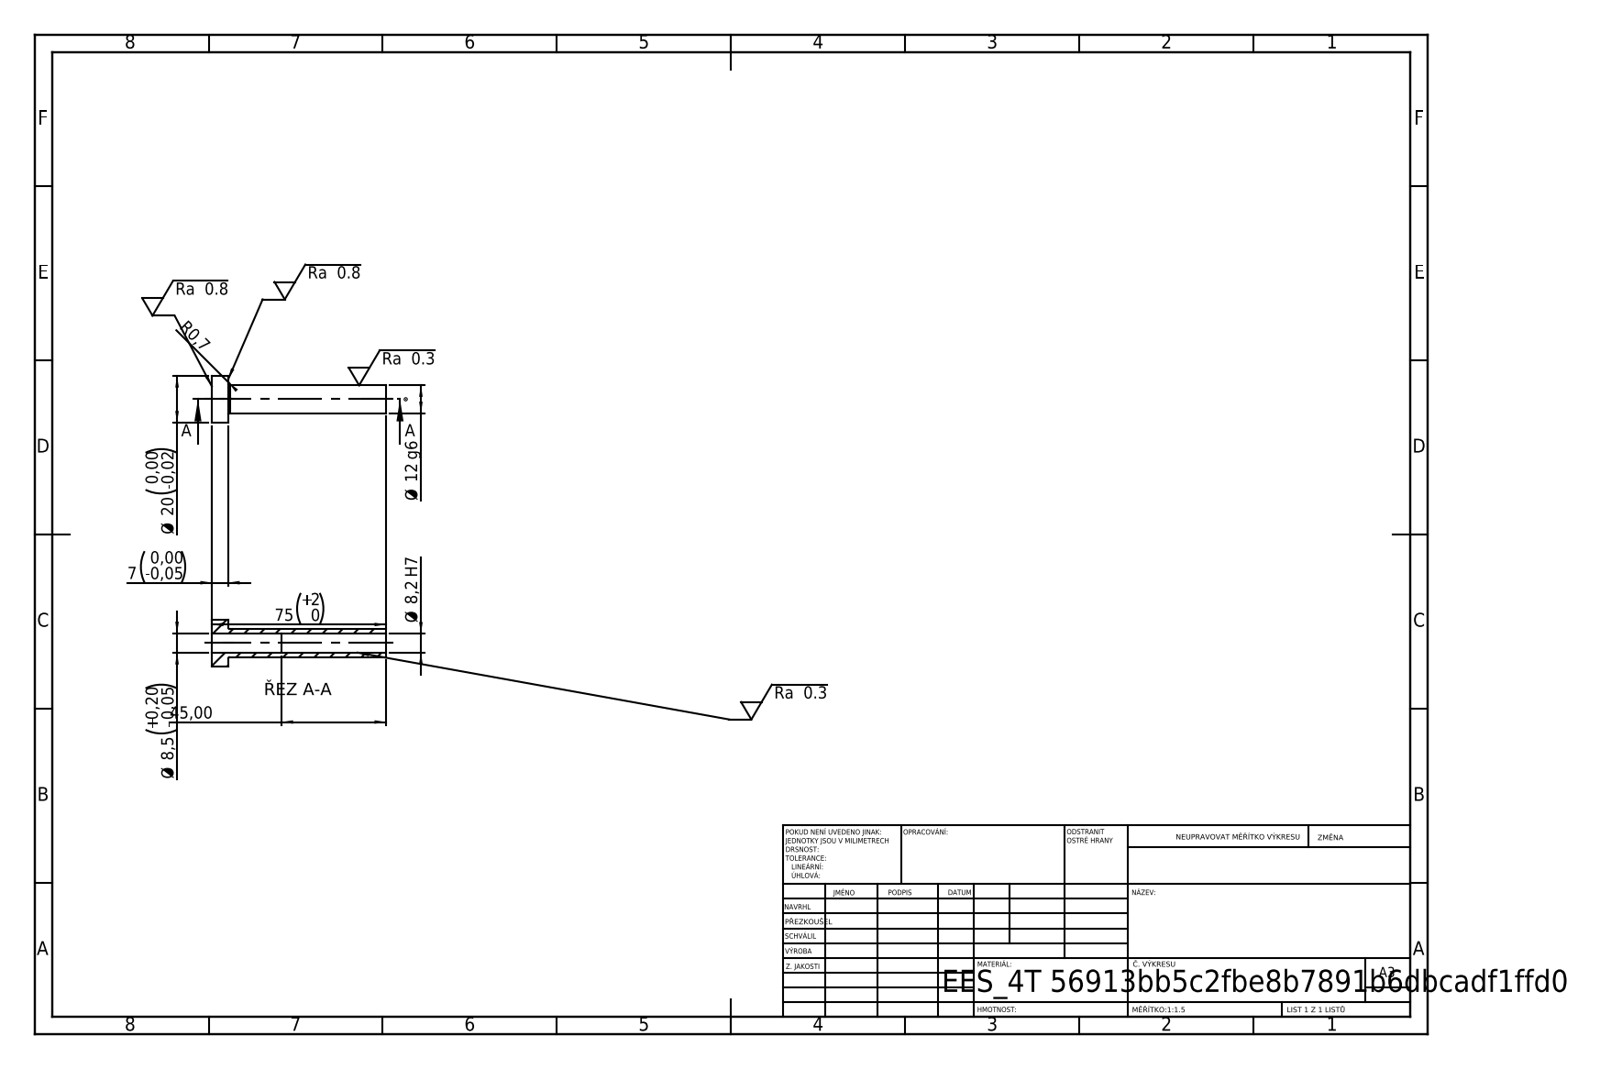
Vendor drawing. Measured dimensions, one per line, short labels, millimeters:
written by: SolidWorks 2019 (CONFIG_CONTROL_DESIGN)
unit: mm
bodies: 1 solid, 14 faces (4 planar, 8 cylindrical, 2 other)
size: 75 × 20 × 20
volume: 5 815 mm³; area: 5 475 mm²
holes: 1× ⌀8.2, 1× ⌀8.5
bosses: 1× ⌀20, 1× ⌀12
face distances: 7, 75, 68, 30, 23, 45
